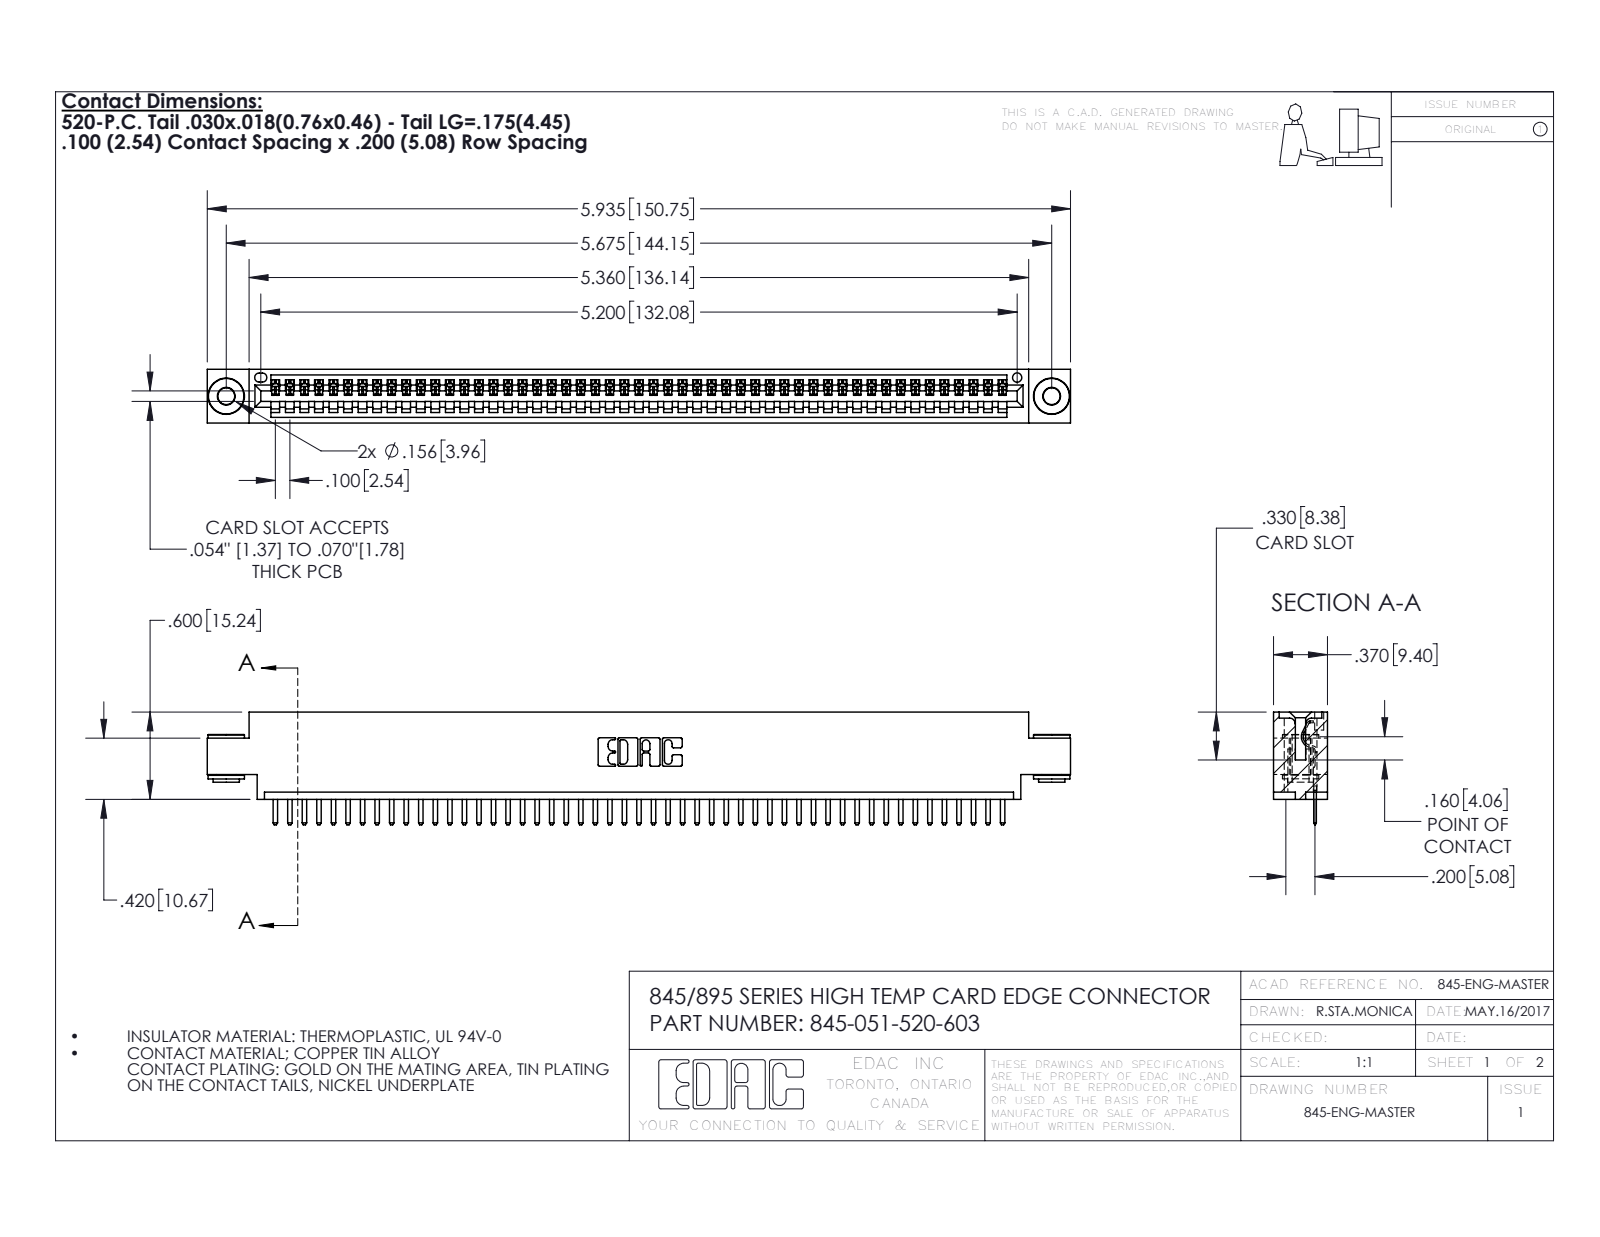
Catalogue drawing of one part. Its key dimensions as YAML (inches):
part_name: "345-250-002_345-250-002-102; 345 Part_0.170 Offset - 0.156 Dia-TH; 345-292-001_345-293-120; 345-051-520-603"
step_written_by: "SolidWorks 2016 (CONFIG_CONTROL_DESIGN)"
units: inches
bodies: {solids: 54, faces: 3330, planar: 2236, cylindrical: 1086, other: 8}
overall_size: [5.935, 0.775, 0.37]
volume: 0.864
surface_area: 29.12
round_holes:
  - {diameter: 0.116, count: 2}
  - {diameter: 0.156, count: 2}
  - {diameter: 0.064, count: 1}
round_bosses_or_shafts:
  - {diameter: 0.25, count: 2}
  - {diameter: 0.18, count: 2}
  - {diameter: 0.136, count: 2}
partial_cylinders:
  - {radius: 0.01, count: 104}
  - {radius: 0.006, count: 102}
  - {radius: 0.01, count: 22}
  - {radius: 0.007, count: 6}
  - {radius: 0.031, count: 6}
  - {radius: 0.026, count: 3}
  - {radius: 0.031, count: 2}
  - {radius: 0.04, count: 2}
face_to_face_distances: [0.072, 0.298, 0.37, 0.2, 0.098, 0.272, 0.025, 0.225, 0.072, 0.175]
hole_center_spacings: [0.27, 5.439, 5.675]
